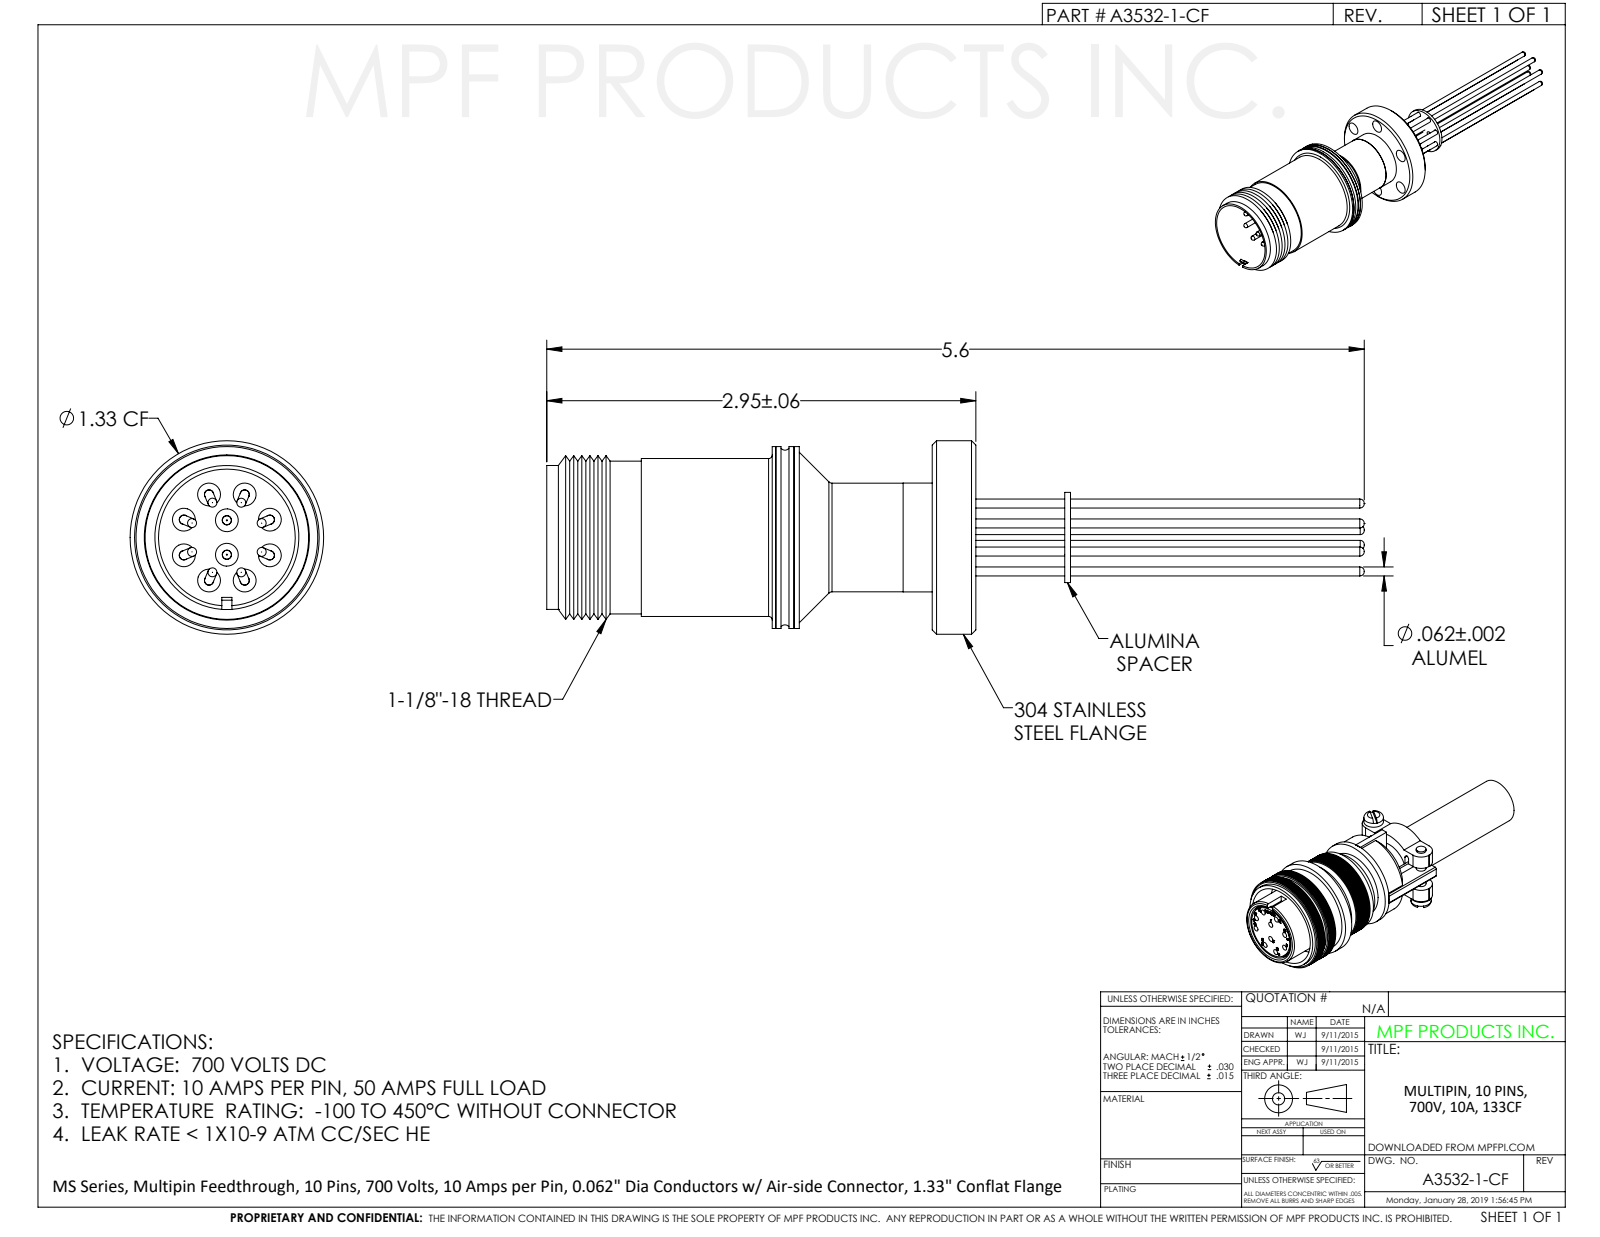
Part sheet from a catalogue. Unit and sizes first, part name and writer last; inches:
Units: inches
Overall size (bounding box): 5.655 × 1.33 × 1.33
Round holes (diameter × count): ⌀0.06 ×10, ⌀0.063 ×10, ⌀0.064 ×10, ⌀0.141 ×10, ⌀0.157 ×10, ⌀0.159 ×10, ⌀0.172 ×6, ⌀0.63 ×1, ⌀0.675 ×1, ⌀0.725 ×1, ⌀0.845 ×1, ⌀0.94 ×1
Round bosses / shafts (diameter × count): ⌀0.062 ×46, ⌀0.187 ×10, ⌀0.157 ×10, ⌀1.33 ×1, ⌀1.25 ×1, ⌀1.085 ×1, ⌀1.05 ×1, ⌀1.02 ×1
Main face-to-face distances: 0.125, 0.965, 1.09, 0.285, 1.25, 1.375, 1.755, 1.47, 0.505, 0.38
Hole centre spacings: 0.41, 0.531, 0.531, 0.193, 0.225, 0.245, 0.32, 0.357
Volume: 1.038 in³ · Surface area: 45.39 in²
Bodies: 35 solids, 526 faces (78 planar, 308 cylindrical, 140 other)
Part name (STEP PRODUCT): A3532-1-CF
STEP written by: SolidWorks 2012 (CONFIG_CONTROL_DESIGN)
